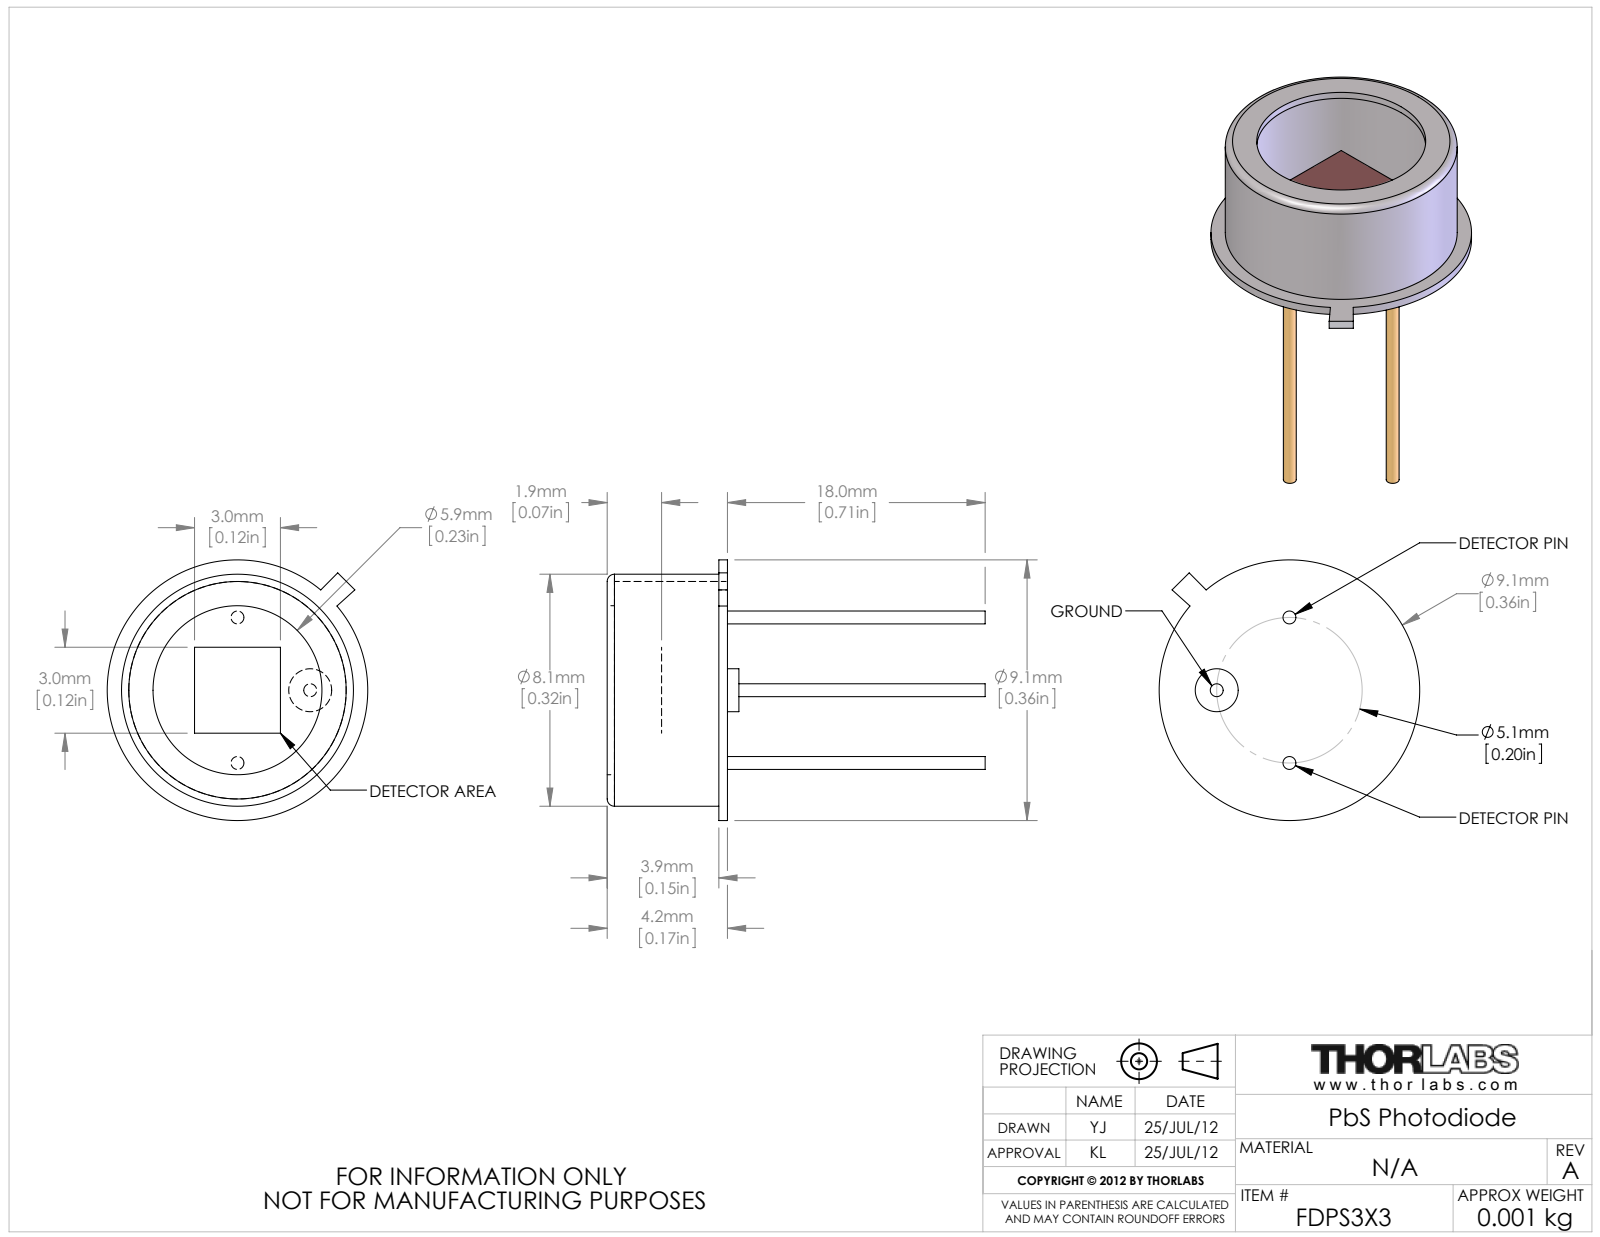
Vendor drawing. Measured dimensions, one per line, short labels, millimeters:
name: 24700-E0W
written by: SolidWorks 2011 (AUTOMOTIVE_DESIGN)
unit: mm
bodies: 2 solids, 37 faces (18 planar, 17 cylindrical, 2 other)
size: 9.1 × 9.1 × 7.25
volume: 44 mm³; area: 409 mm²
holes: 1× ⌀5.9, 1× ⌀7.59
bosses: 3× ⌀0.45, 1× ⌀9.1, 1× ⌀8.1, 1× ⌀1.5
face distances: 3.9, 3.95, 4.2, 4.15, 3.65, 1.79, 2.3, 1.74, 2.25, 1.49
